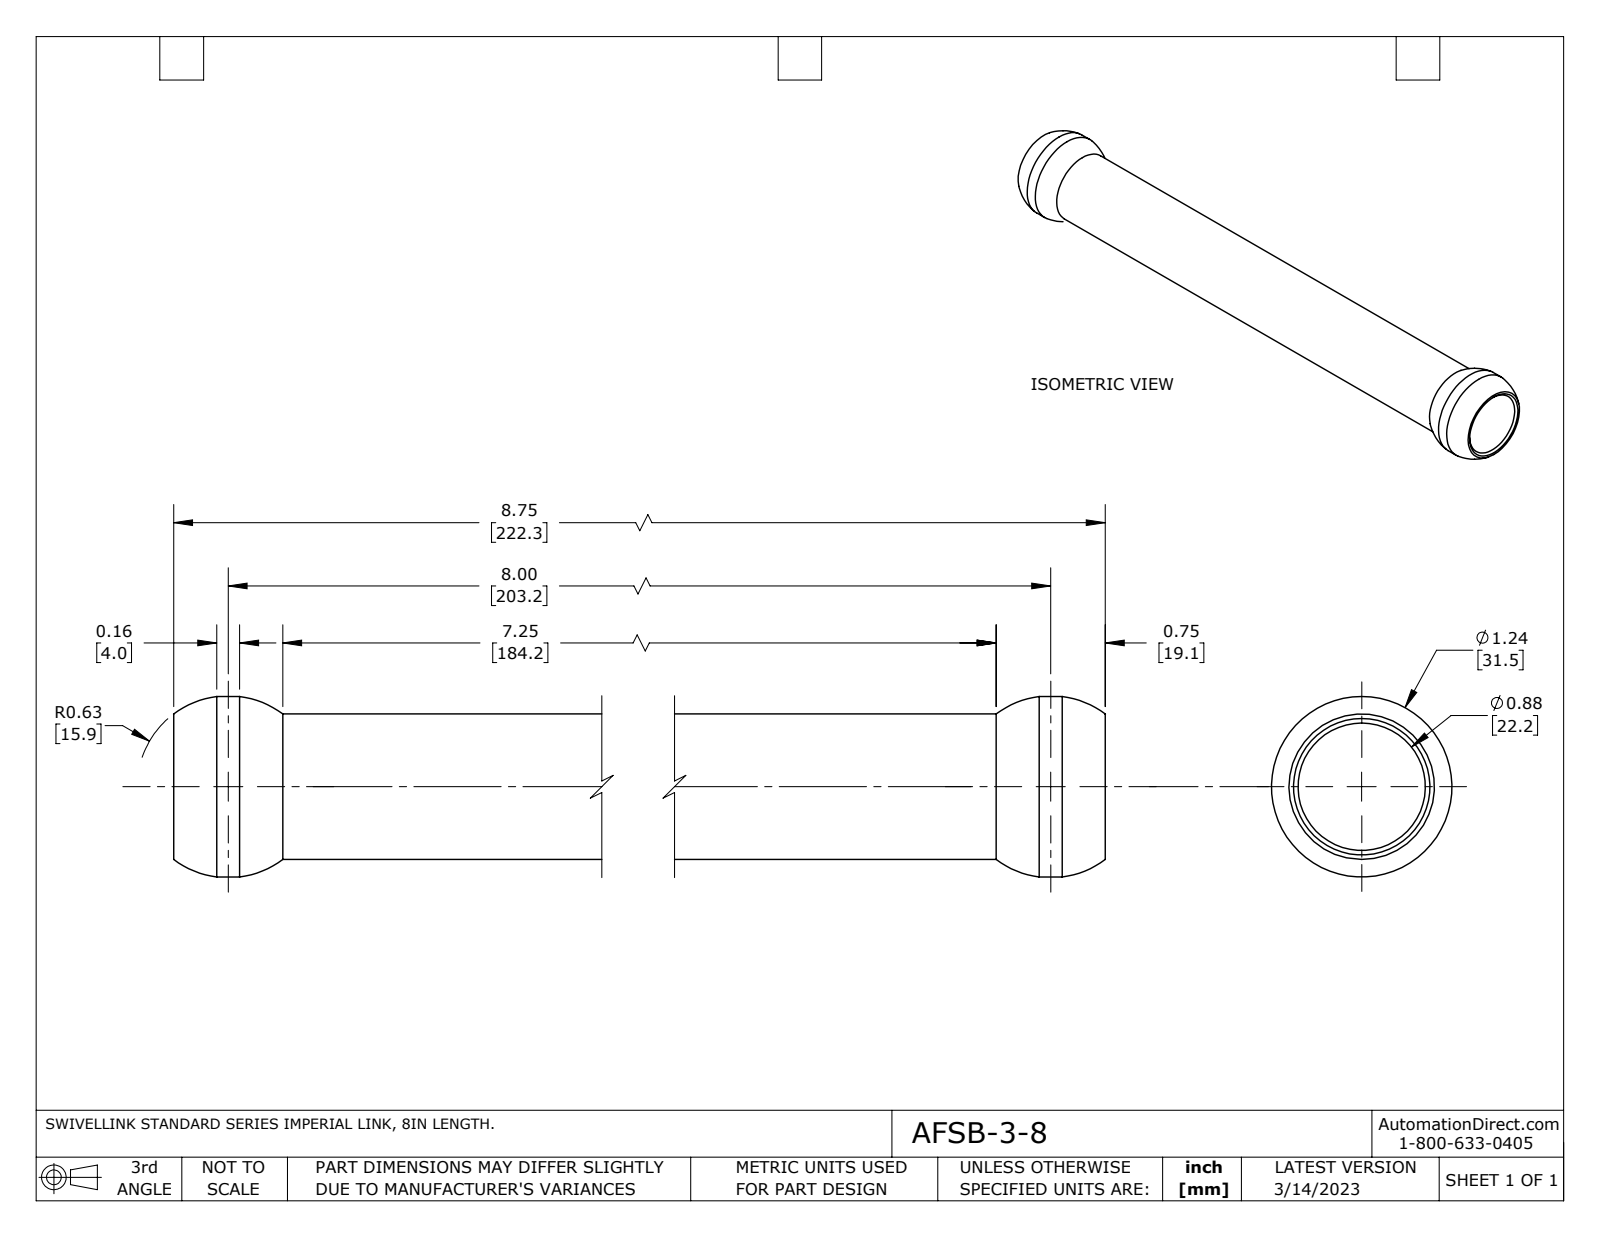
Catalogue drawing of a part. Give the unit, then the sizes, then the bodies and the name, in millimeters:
Units: millimetres
Overall size (bounding box): 222.3 × 31.5 × 31.5
Round holes (diameter × count): ⌀22.2 ×1
Round bosses / shafts (diameter × count): ⌀31.5 ×1, ⌀25.4 ×1
Main face-to-face distances: 222.3
Volume: 33 460 mm³ · Surface area: 34 170 mm²
Bodies: 1 solid, 12 faces (2 planar, 4 cylindrical, 6 other)
Part name (STEP PRODUCT): AFSB-3-8
STEP written by: SolidWorks 2021 (AUTOMOTIVE_DESIGN)
